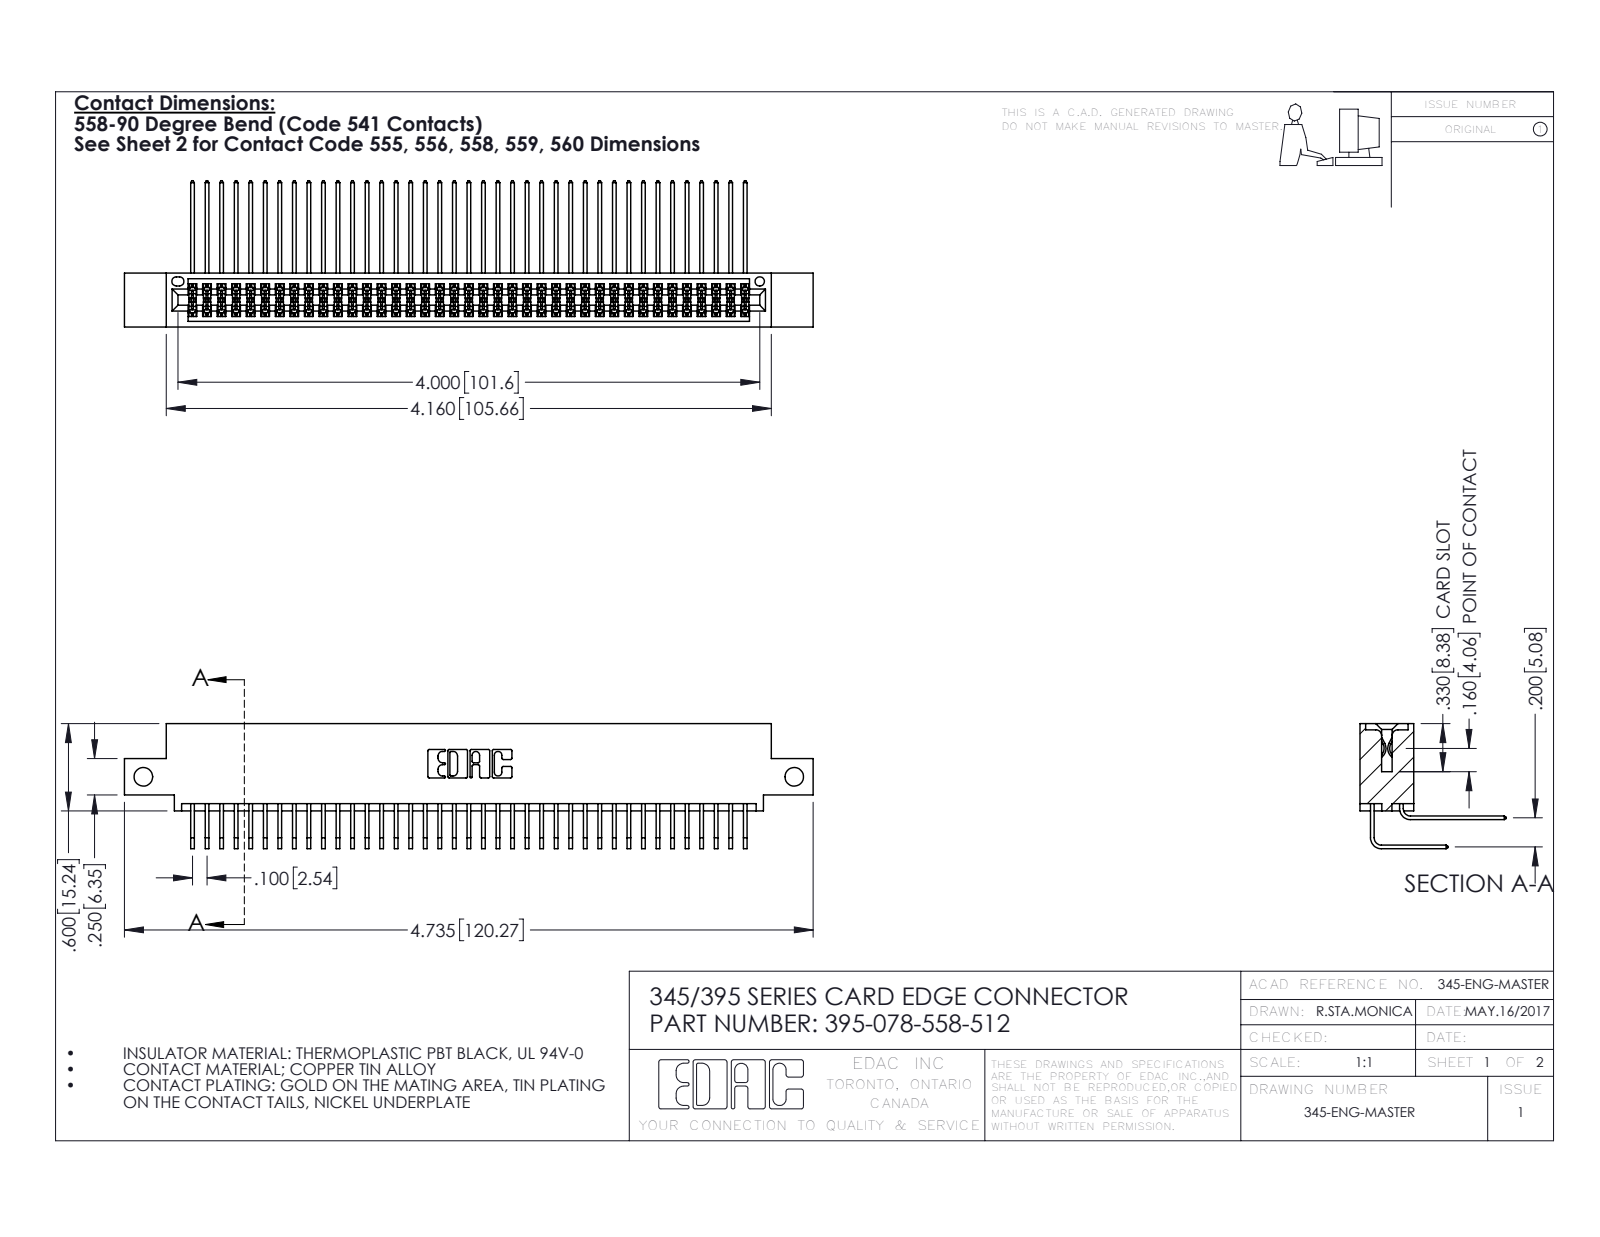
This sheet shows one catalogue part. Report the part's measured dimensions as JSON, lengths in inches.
{"part_name": "345-292-001_558 559 Tail - 1; 345 Part_0.110 Offset - Side Mount; 395-078-558-512; 345-292-001_558 Tail - 2", "step_written_by": "SolidWorks 2016 (CONFIG_CONTROL_DESIGN)", "units": "inches", "bodies": {"solids": 79, "faces": 4186, "planar": 2814, "cylindrical": 1372, "other": 0}, "overall_size": [4.735, 1.005, 0.859], "volume_in3": 0.729, "surface_area_in2": 30.49, "round_holes": [[0.128, 2], [0.064, 1]], "partial_cylinders_radius": [[0.006, 118], [0.01, 22], [0.007, 6], [0.031, 6], [0.026, 3], [0.014, 2], [0.019, 2], [0.022, 2]], "face_to_face_distances": [0.072, 0.298, 0.2, 0.37, 0.098, 0.272, 0.025, 0.225, 0.025, 0.175], "hole_center_spacings": [4.475]}
